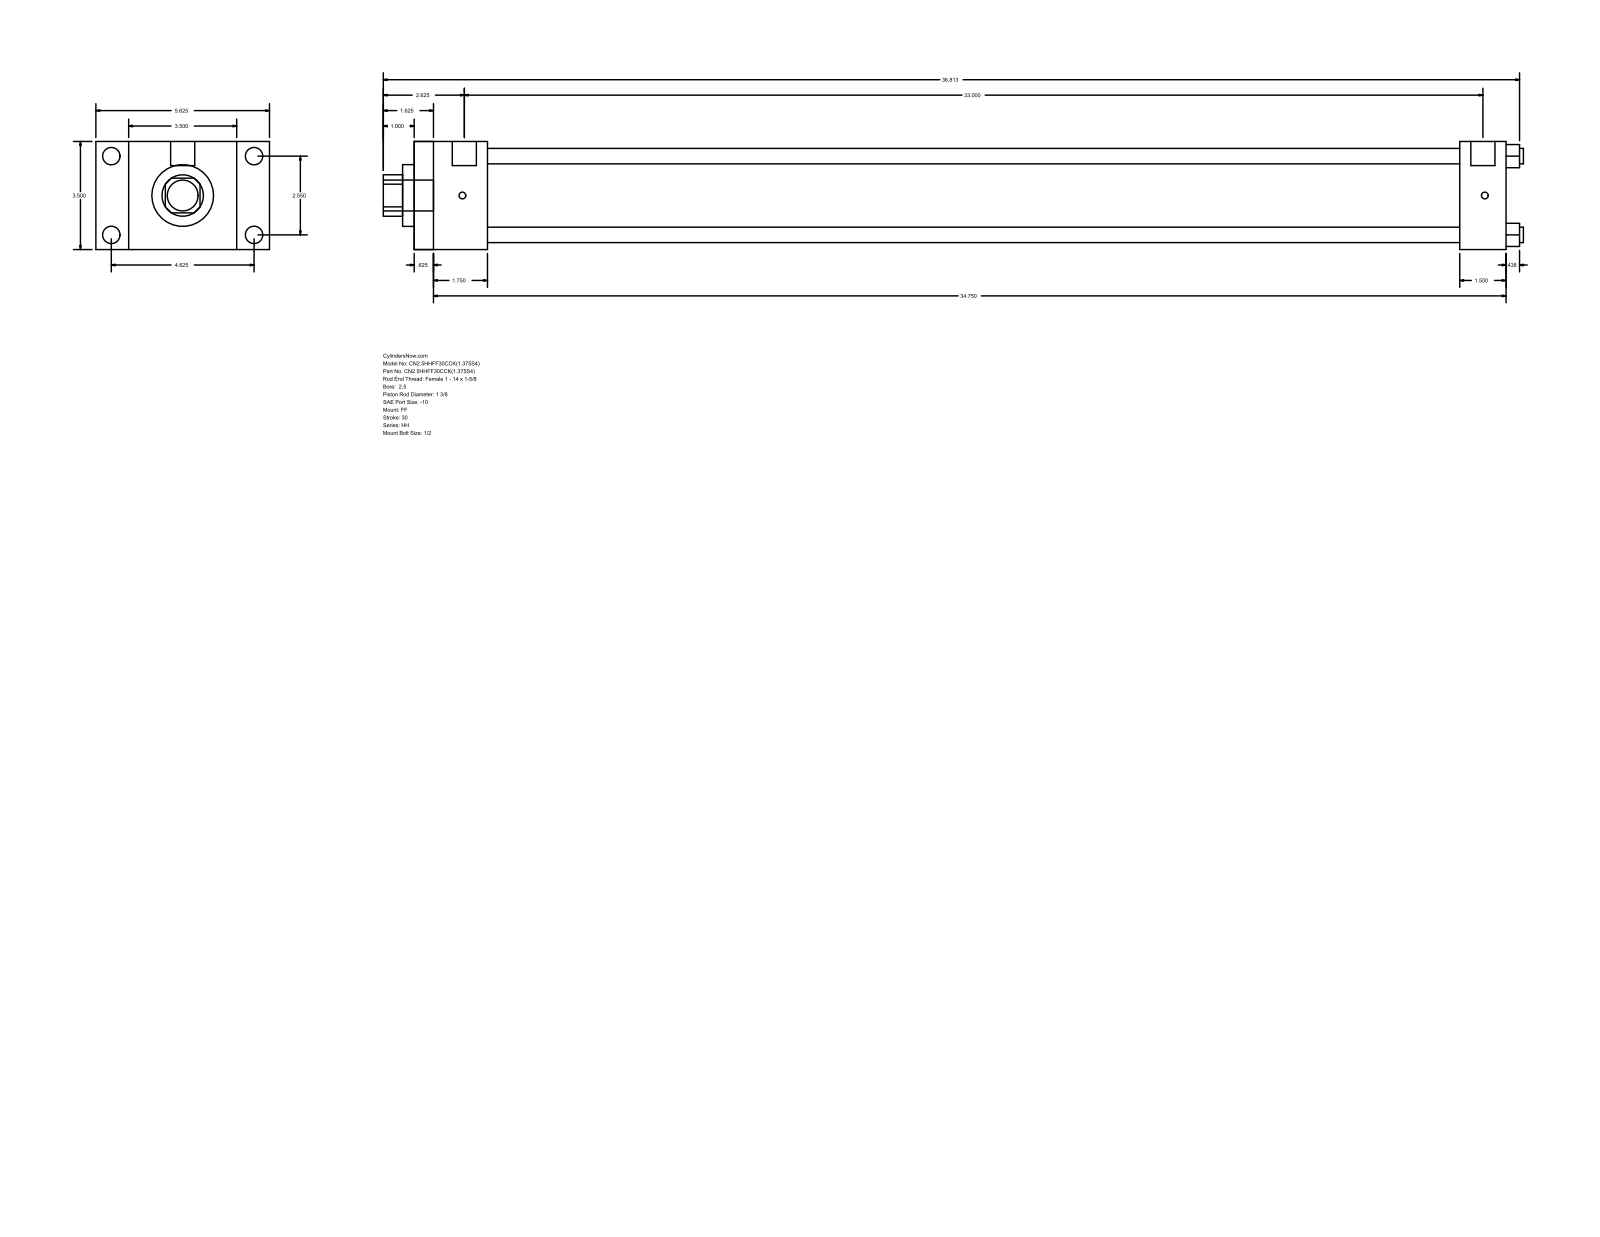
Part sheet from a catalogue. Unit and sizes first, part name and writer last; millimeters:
Units: millimetres
Overall size (bounding box): 938.21 × 142.88 × 88.9
Round holes (diameter × count): ⌀12.7 ×4, ⌀34.92 ×1, ⌀50.8 ×1, ⌀73.03 ×1
Round bosses / shafts (diameter × count): ⌀14.3 ×4, ⌀5.56 ×4, ⌀19.84 ×2, ⌀25.4 ×1
Partial cylindrical surfaces — rounded edges, fillets, slot ends (radius × count): R17.06 ×1
Main face-to-face distances: 88.9, 898.52, 15.87, 882.65, 60.32, 44.45, 838.2, 860.43, 844.56, 800.11
Hole centre spacings: 45.79, 64.76, 91.58
Bodies: 0 solids, 92 faces (64 planar, 28 cylindrical, 0 other)
Part name (STEP PRODUCT): HH_FF__0250_1.375
STEP written by: GSSL Pune (CONFIG_CONTROL_DESIGN)
